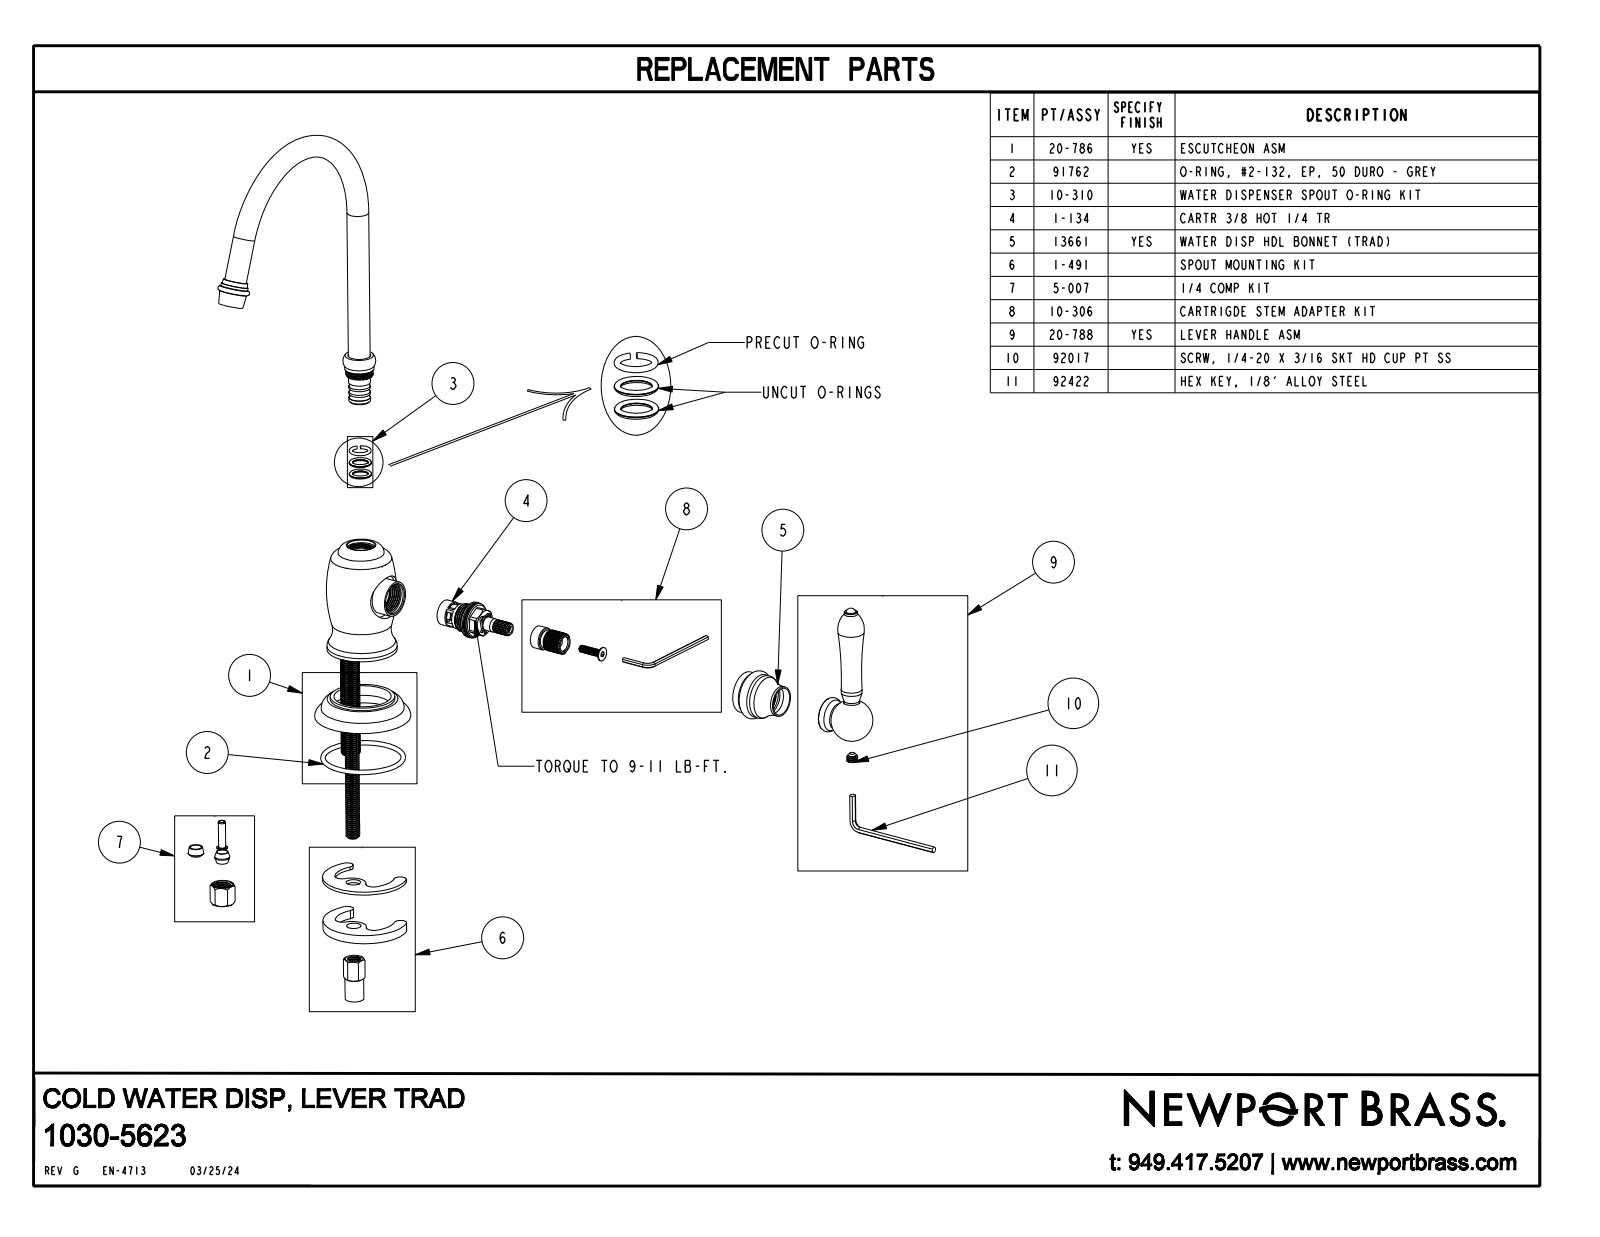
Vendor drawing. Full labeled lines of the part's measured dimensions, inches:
Part name (STEP PRODUCT): 1030-5623
STEP written by: CREO PARAMETRIC BY PTC INC, 2018400 (CONFIG_CONTROL_DESIGN)
Units: inches
Bodies: 1 solid, 84 faces (10 planar, 24 cylindrical, 50 other)
Overall size (bounding box): 9.455 × 6.182 × 3.818
Volume: 9.426 in³ · Surface area: 48.54 in²
Round holes (diameter × count): ⌀1 ×1
Round bosses / shafts (diameter × count): ⌀0.5 ×2, ⌀0.3 ×2, ⌀1.61 ×1, ⌀0.95 ×1, ⌀0.675 ×1, ⌀0.625 ×1, ⌀0.6 ×1, ⌀0.48 ×1
Main face-to-face distances: 0.02, 3.255, 1.02, 1, 0.575, 0.475, 0.1, 0.425, 2.83, 4.473
